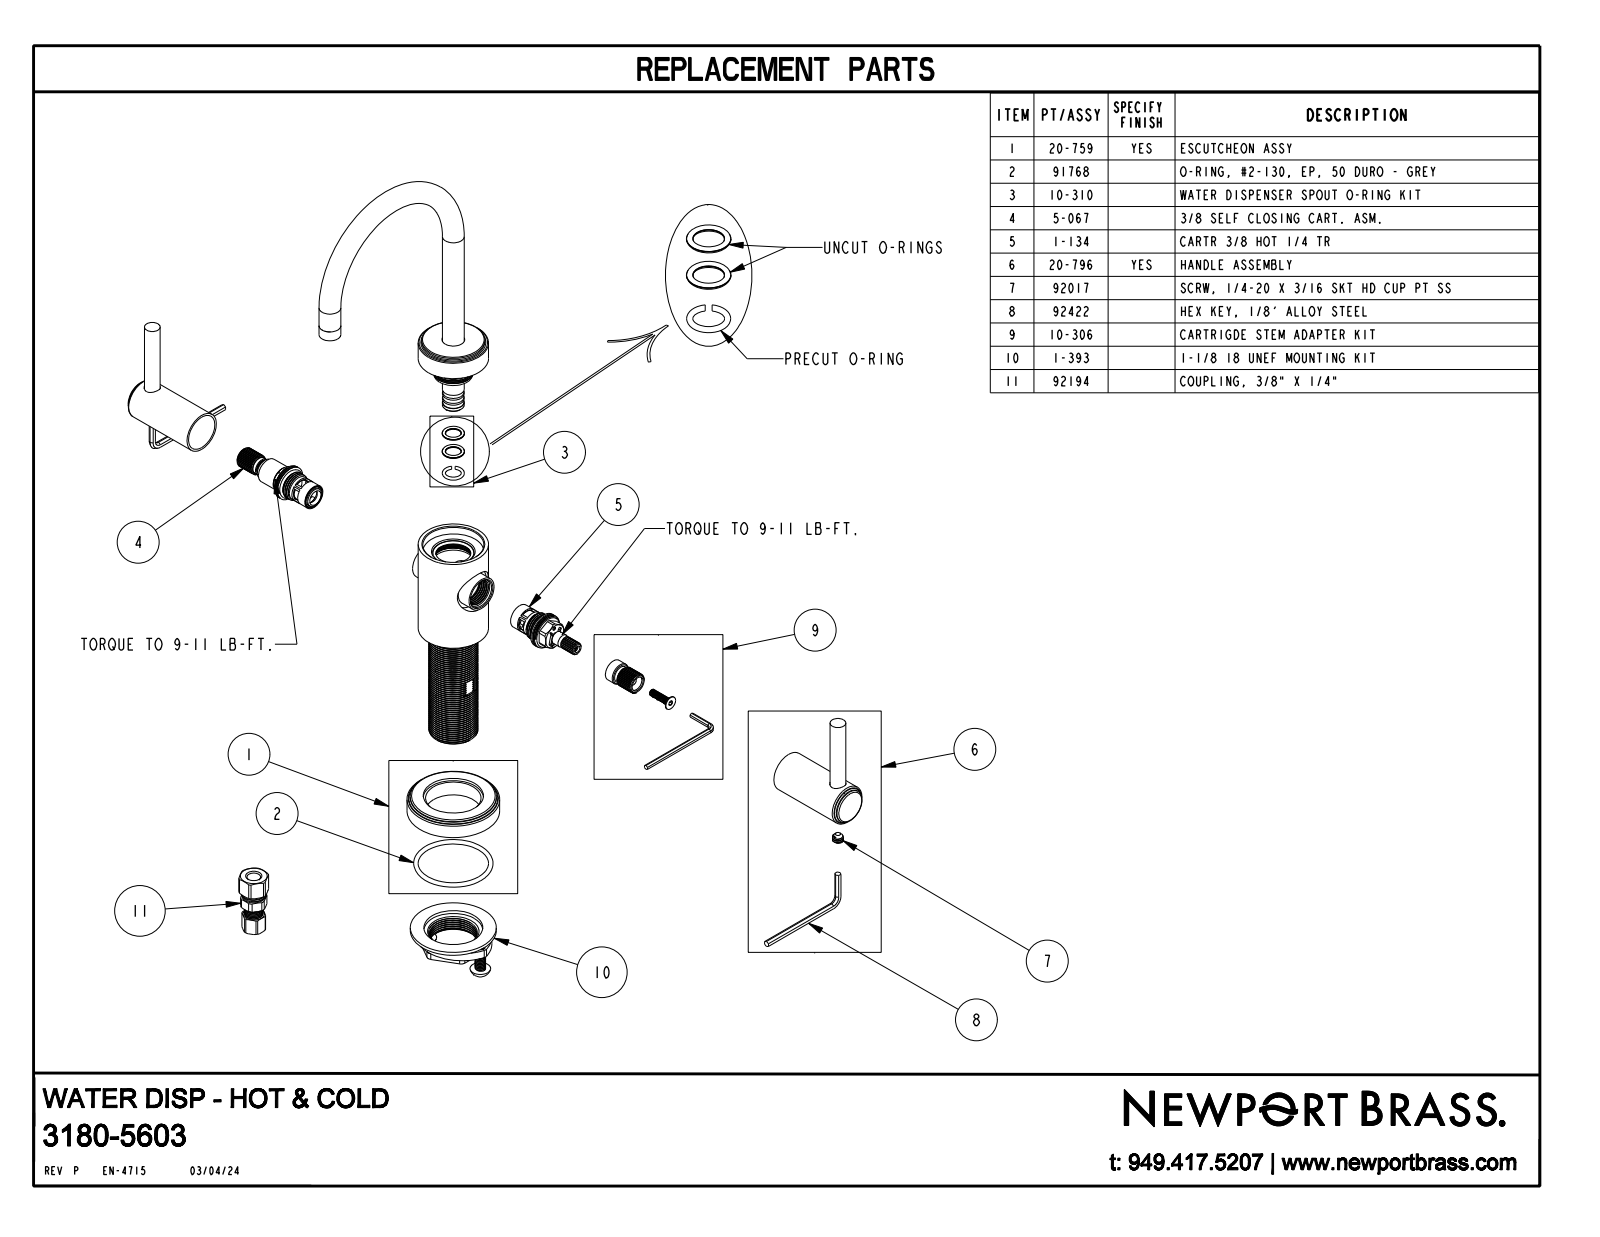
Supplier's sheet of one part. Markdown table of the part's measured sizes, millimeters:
| quantity | value |
| --- | --- |
| part name | 3180-5603 |
| STEP written by | CREO PARAMETRIC BY PTC INC, 2018400 (CONFIG_CONTROL_DESIGN) |
| units | millimeters |
| bodies | 1 solid, 74 faces (16 planar, 32 cylindrical, 26 other) |
| overall size | 235.6 × 135 × 132.6 |
| volume | 201 400 mm³ |
| surface area | 37 240 mm² |
| round holes (diameter × count) | 9.5 × 2, 25.4 × 1 |
| round bosses / shafts (diameter × count) | 12.7 × 2, 9.1 × 2, 54 × 1, 50.2 × 1, 40.9 × 1, 36.8 × 1, 24.1 × 1, 20.3 × 1 |
| main face-to-face distances | 84, 10.8, 73.2, 132.6, 104.6, 93.8, 20.6, 165.7, 154.9, 81.8 |
| hole center spacings | 112.9 |
